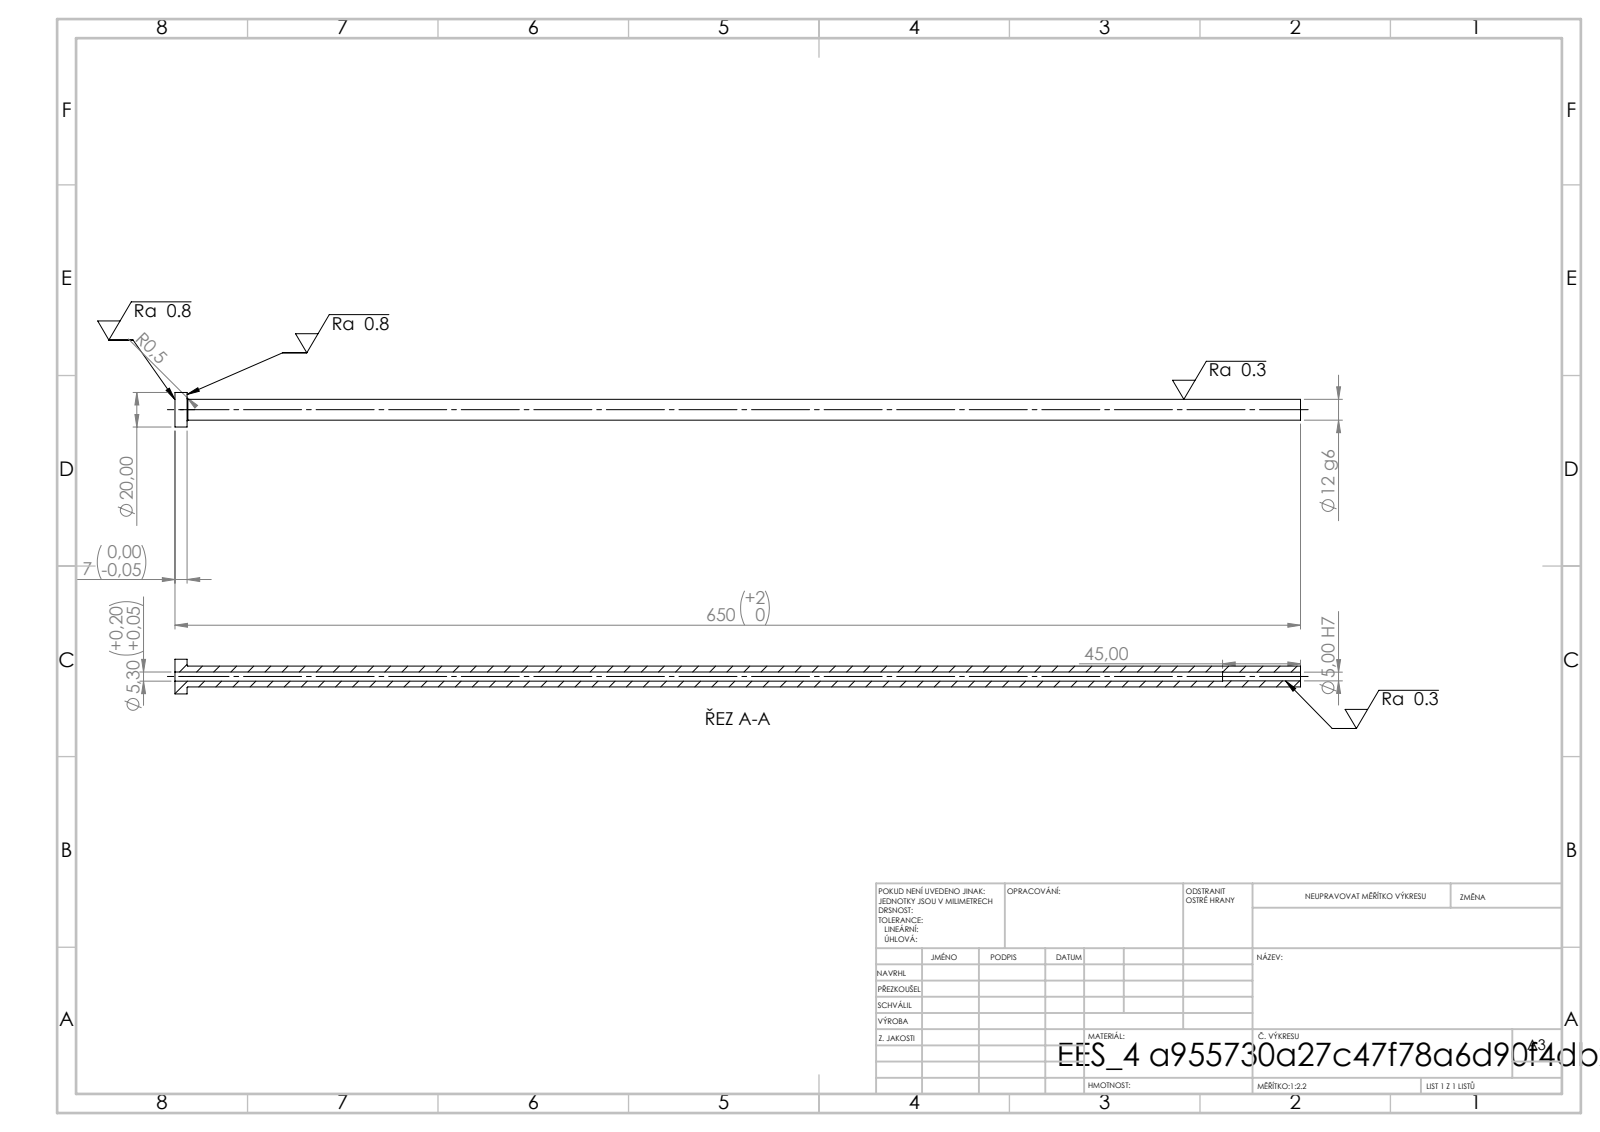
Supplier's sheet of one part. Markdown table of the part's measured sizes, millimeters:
| quantity | value |
| --- | --- |
| STEP written by | SolidWorks 2019 (CONFIG_CONTROL_DESIGN) |
| units | millimeters |
| bodies | 1 solid, 14 faces (4 planar, 8 cylindrical, 2 other) |
| overall size | 650 × 20 × 20 |
| volume | 60 692 mm³ |
| surface area | 36 042 mm² |
| round holes (diameter × count) | 5 × 1, 5.3 × 1 |
| round bosses / shafts (diameter × count) | 20 × 1, 12 × 1 |
| main face-to-face distances | 7, 650, 643, 605, 598, 45 |
